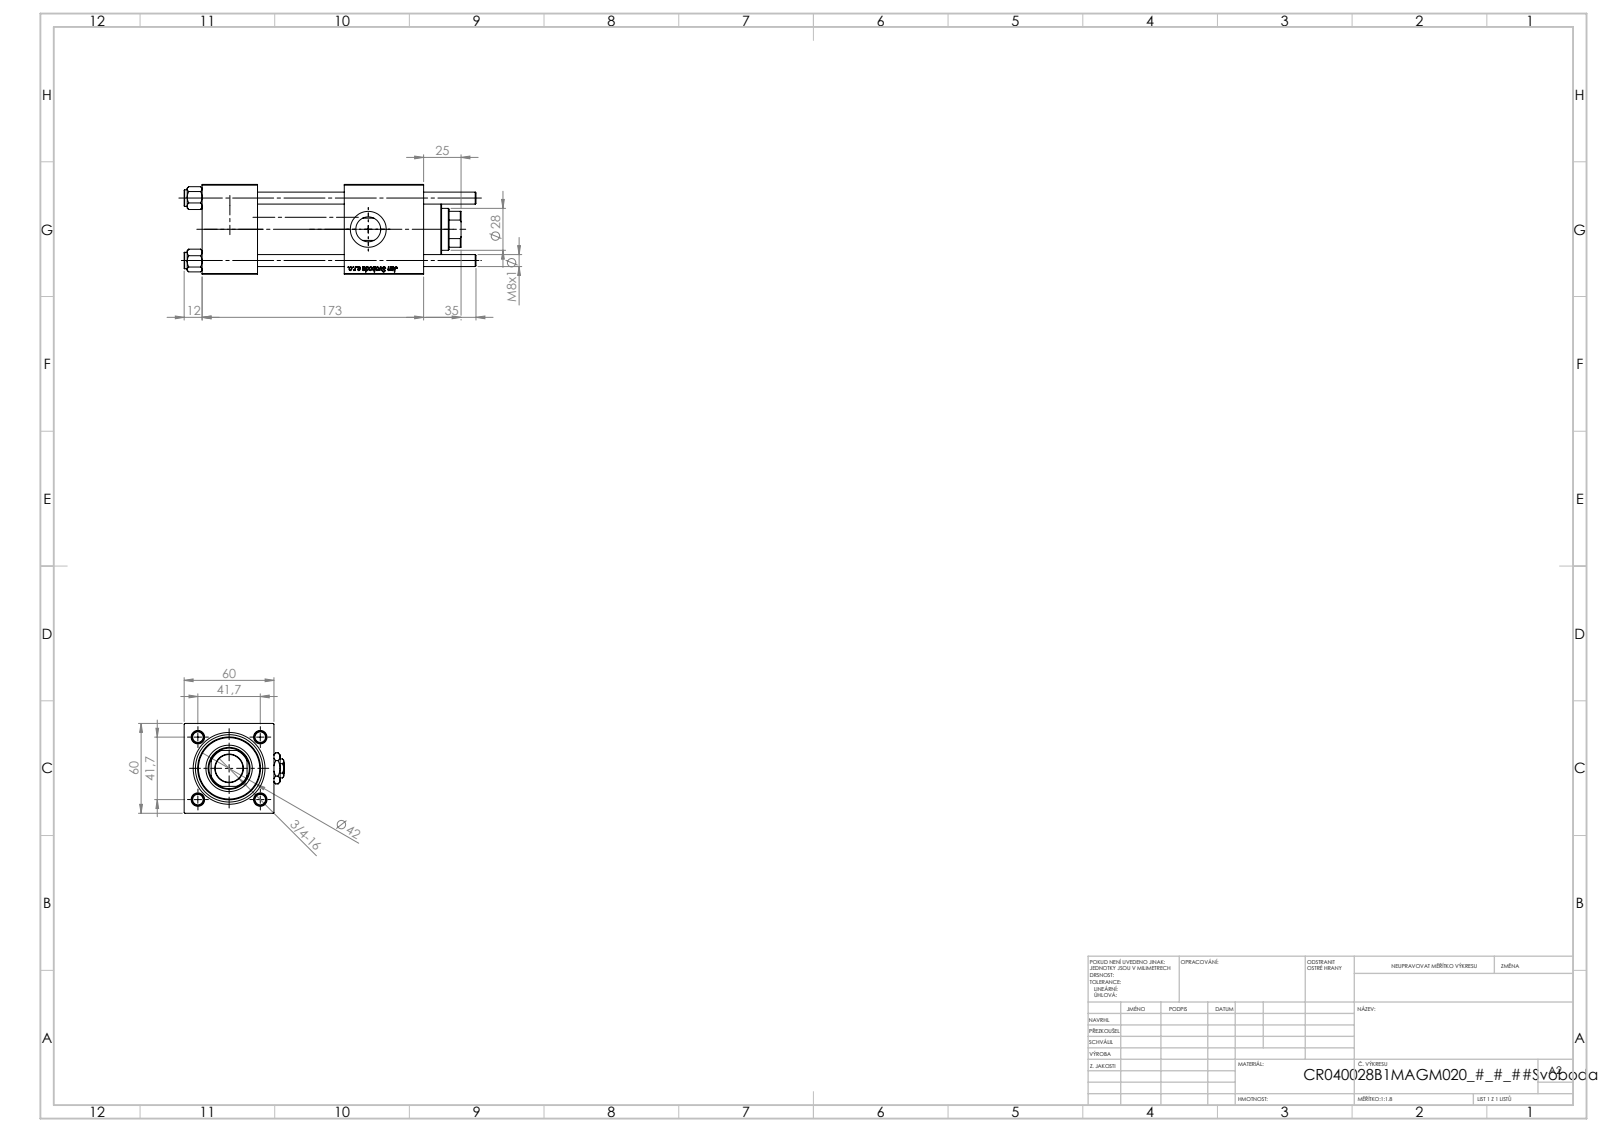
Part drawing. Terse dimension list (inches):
name: V215CR_VCP_B; V215CR_B_TYCINKA; Zatka_pro_OIL_PORT; V215_VC_A (+2 more)
written by: SolidWorks 2019 (CONFIG_CONTROL_DESIGN)
unit: in
bodies: 12 solids, 1207 faces (456 planar, 83 cylindrical, 668 other)
size: 7.677 × 2.638 × 2.362
volume: 26.45 in³; area: 187.9 in²
holes: 4× ⌀0.315, 2× ⌀0.276, 2× ⌀0.656, 1× ⌀0.63, 1× ⌀0.728, 1× ⌀0.945, 1× ⌀1.102, 1× ⌀1.22, 1× ⌀1.575, 1× ⌀1.772
bosses: 4× ⌀0.433, 1× ⌀1.811, 1× ⌀1.654
rounds: 1× R0.531
face distances: 2.362, 1.457, 2.283, 3.74, 2.087, 4.697, 3.24, 0.957, 5.827, 4.37
hole spacings: 1.161, 1.642, 2.322
